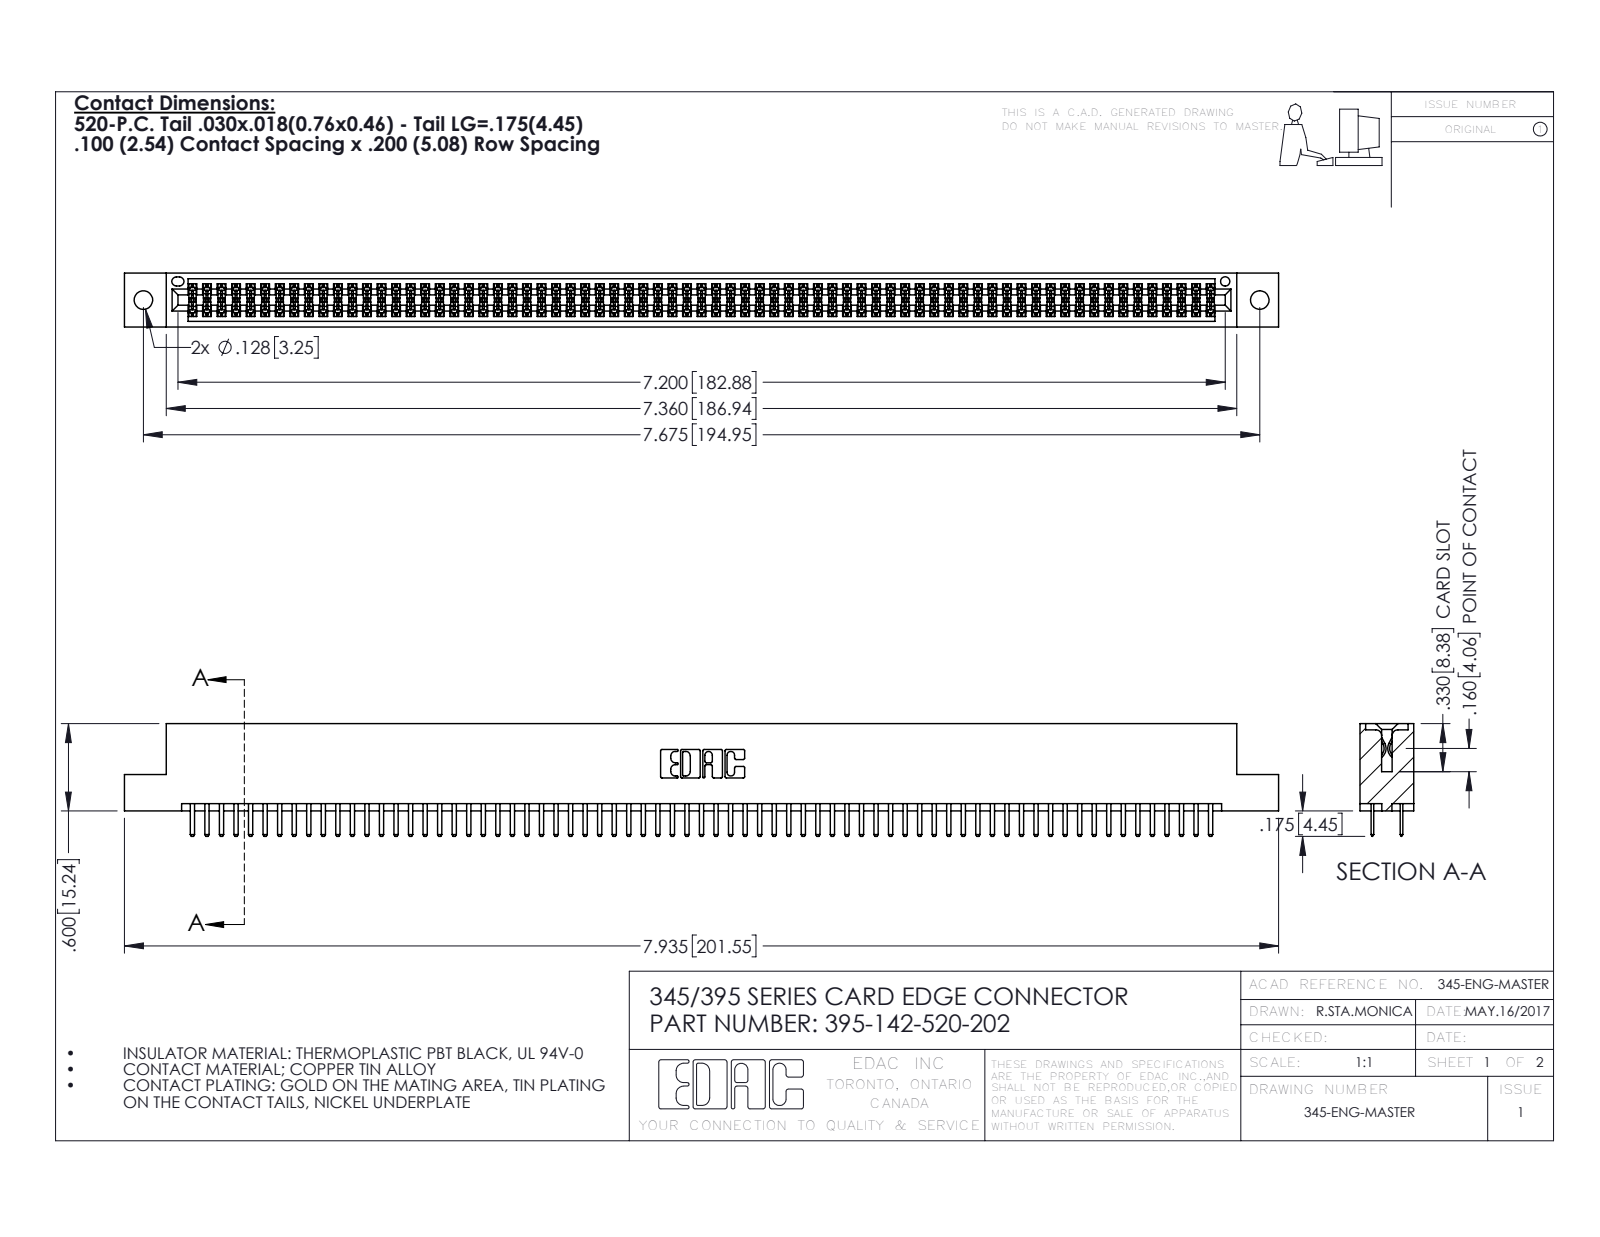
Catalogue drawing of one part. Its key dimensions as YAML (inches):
part_name: "345-292-001_345-293-120; 395-142-520-202; 345 Part_Flush Mounting Lugs - 0.128 Dia"
step_written_by: "SolidWorks 2016 (CONFIG_CONTROL_DESIGN)"
units: inches
bodies: {solids: 143, faces: 7794, planar: 5050, cylindrical: 2744, other: 0}
overall_size: [7.935, 0.775, 0.37]
volume: 1.205
surface_area: 45.49
round_holes:
  - {diameter: 0.128, count: 2}
  - {diameter: 0.064, count: 1}
partial_cylinders:
  - {radius: 0.006, count: 213}
  - {radius: 0.01, count: 146}
  - {radius: 0.01, count: 22}
  - {radius: 0.007, count: 6}
  - {radius: 0.031, count: 6}
  - {radius: 0.026, count: 3}
  - {radius: 0.014, count: 2}
  - {radius: 0.019, count: 2}
face_to_face_distances: [0.298, 0.072, 0.2, 0.37, 0.098, 0.272, 0.025, 0.225, 0.022, 0.072]
hole_center_spacings: [0.27, 7.439, 7.675]
